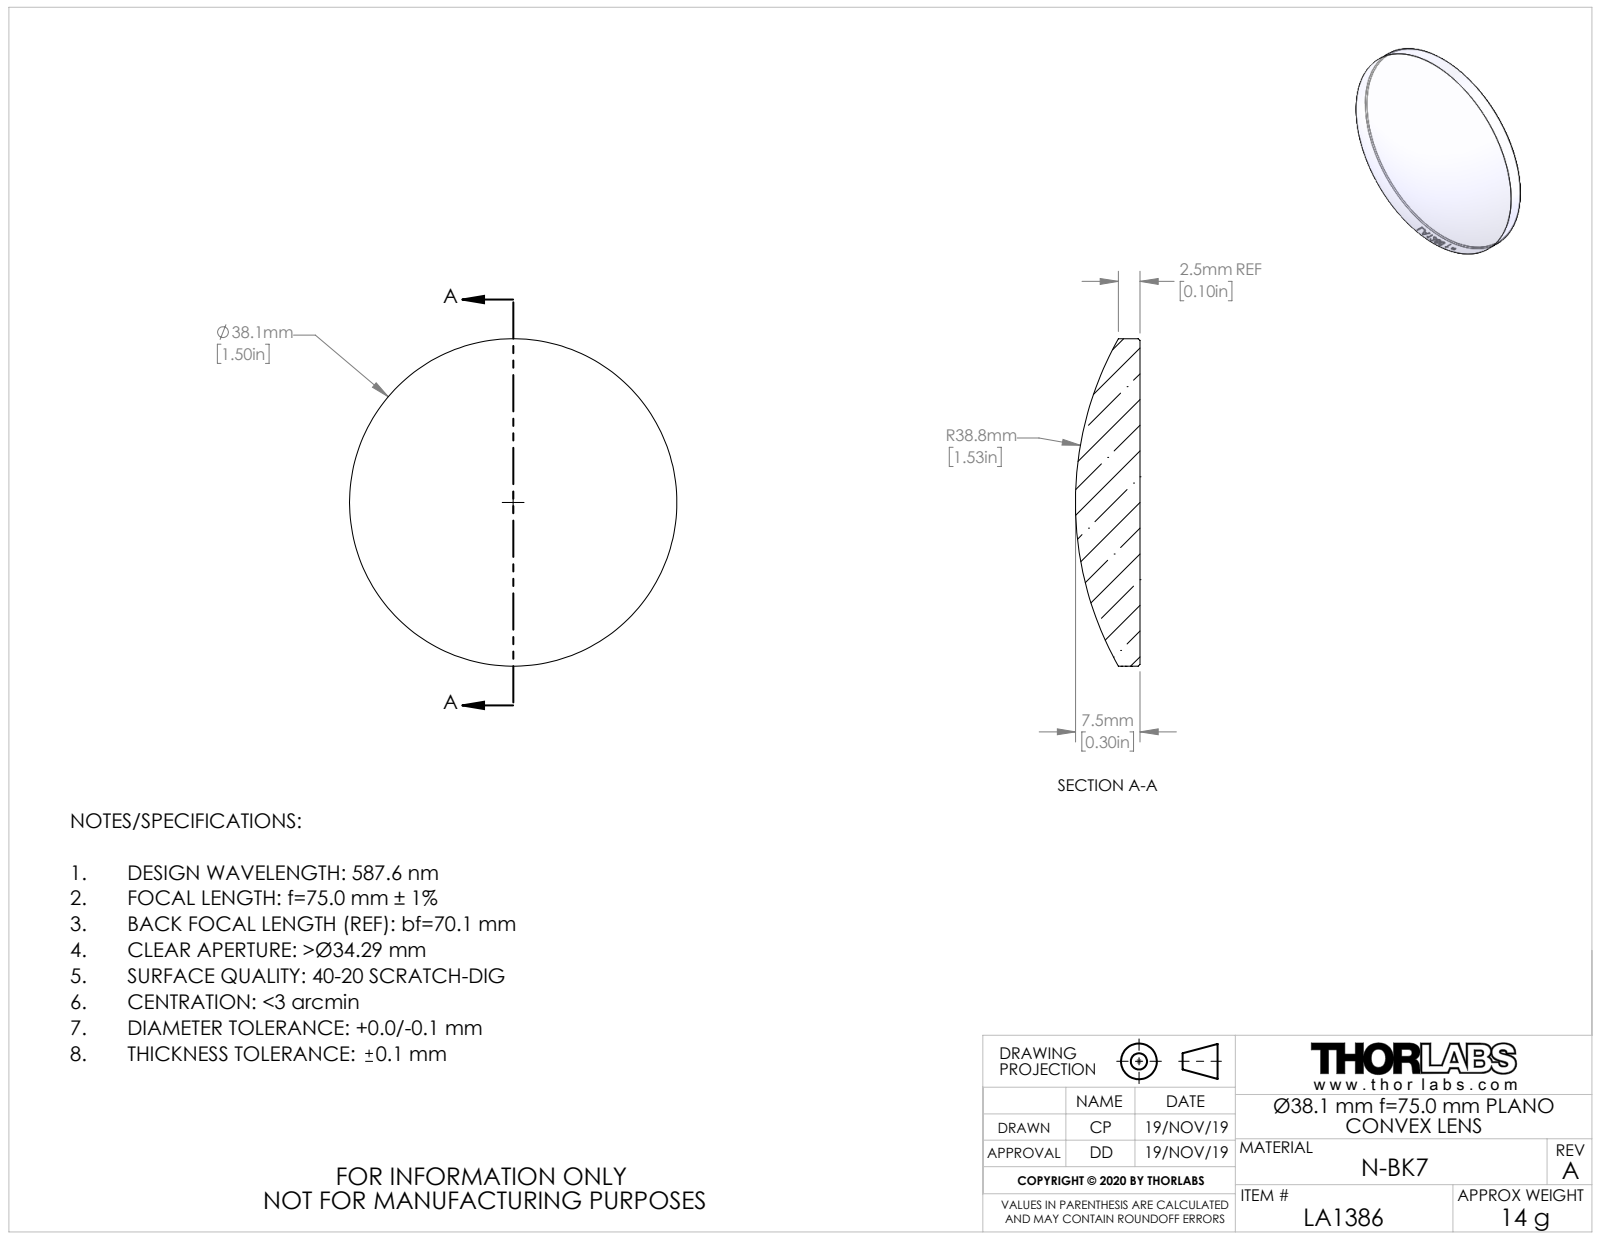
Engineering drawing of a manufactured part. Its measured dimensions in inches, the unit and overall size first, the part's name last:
Units: inches
Overall size (bounding box): 1.5 × 1.5 × 0.295
Round bosses / shafts (diameter × count): ⌀1.5 ×1
Volume: 0.352 in³ · Surface area: 4.098 in²
Bodies: 1 solid, 21 faces (1 planar, 16 cylindrical, 4 other)
Part name (STEP PRODUCT): TTN200653-E0W
STEP written by: SolidWorks 2018 (CONFIG_CONTROL_DESIGN)
